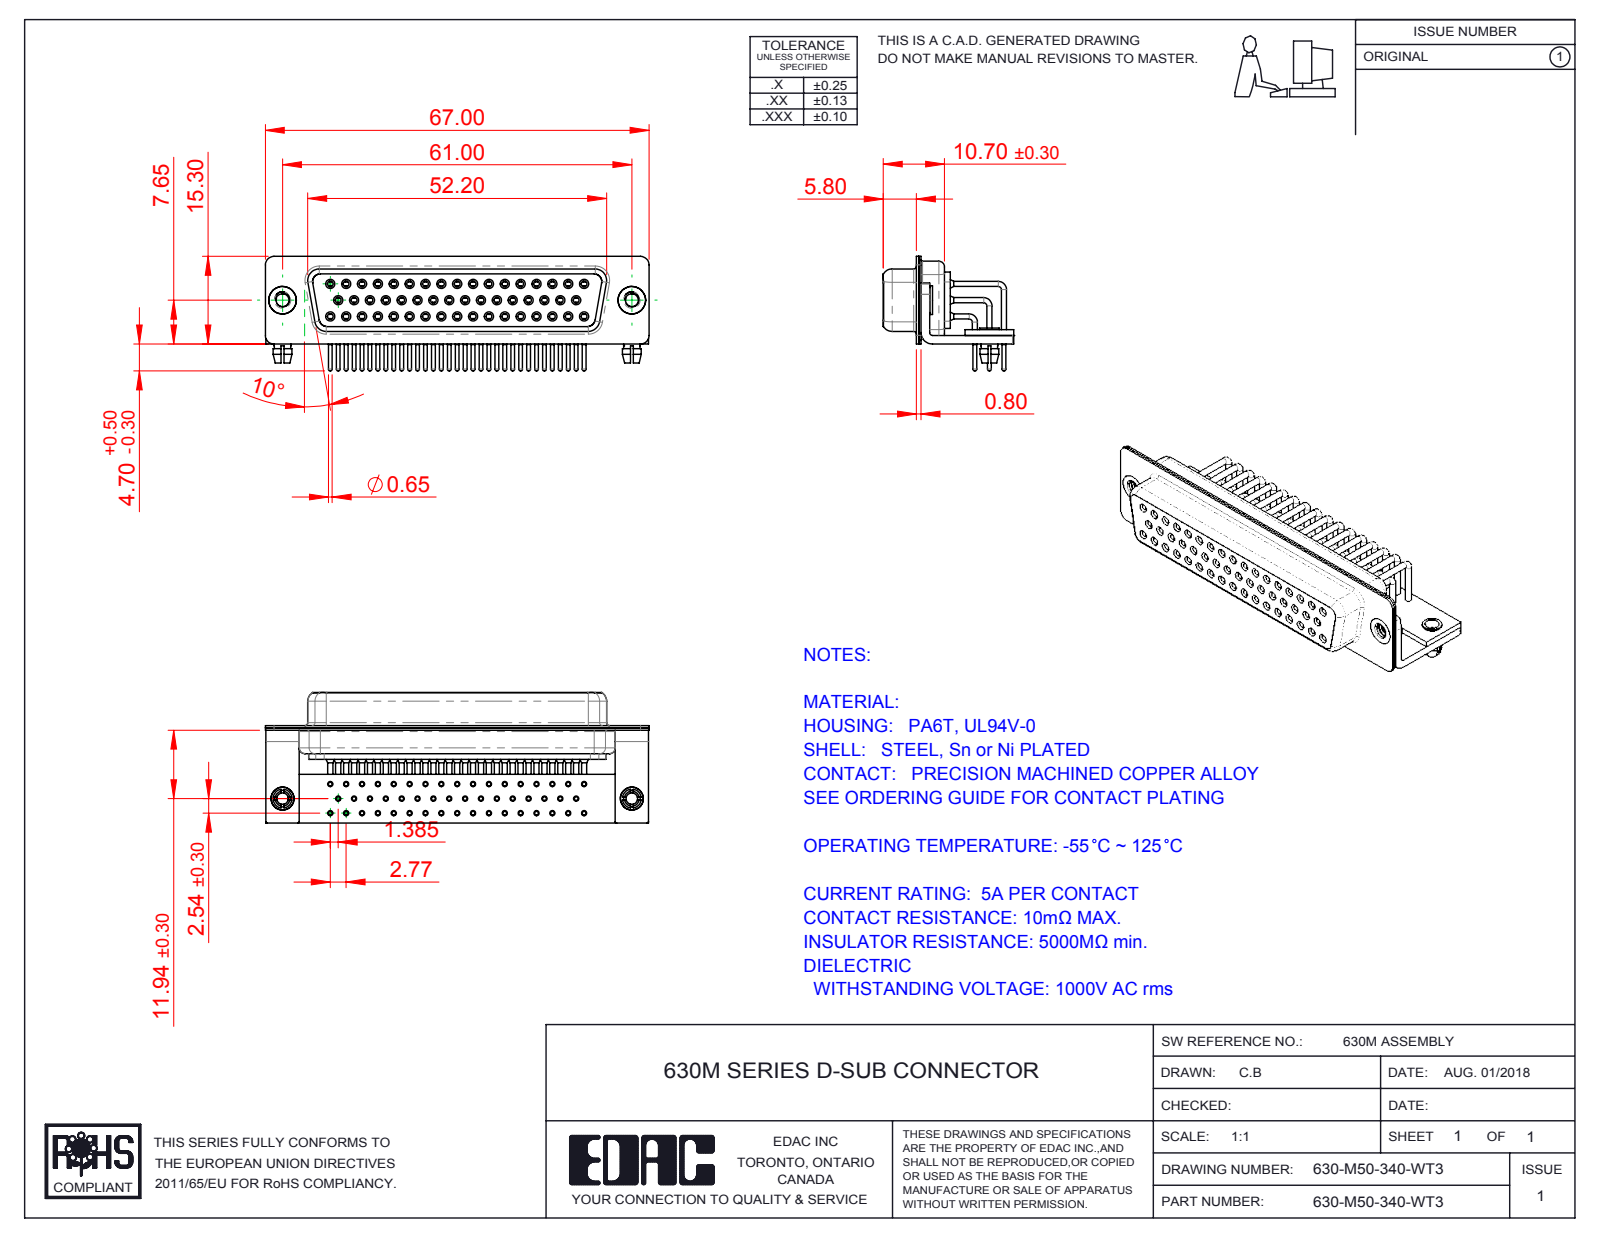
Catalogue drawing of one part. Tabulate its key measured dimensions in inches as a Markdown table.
| quantity | value |
| --- | --- |
| part name | 630M Stabilizer Bracket_50 Contacts; 630M Shell Rear_50 Contacts; 630M Housing_50 Contacts; 630M Contact Row 2_50 Contacts (+7 more) |
| STEP written by | SolidWorks 2016 (CONFIG_CONTROL_DESIGN) |
| units | inches |
| bodies | 60 solids, 3171 faces (891 planar, 1441 cylindrical, 839 other) |
| overall size | 2.638 × 0.898 × 0.787 |
| volume | 0.483 in³ |
| surface area | 29.21 in² |
| round holes (diameter × count) | 0.079 × 52, 0.035 × 50, 0.039 × 50, 0.043 × 50, 0.067 × 50, 0.071 × 50, 0.089 × 2, 0.098 × 2, 0.126 × 2, 0.157 × 2, 0.189 × 2 |
| round bosses / shafts (diameter × count) | 0.035 × 59, 0.063 × 50, 0.059 × 50, 0.026 × 50, 0.197 × 2, 0.193 × 2, 0.157 × 2, 0.134 × 2 |
| partial cylindrical surfaces (radius × count) | 0.01 × 16, 0.059 × 16, 0.079 × 13, 0.053 × 8, 0.063 × 8, 0.02 × 5, 0.024 × 4, 0.026 × 4 |
| main face-to-face distances | 0.016, 0.039, 0.087, 0.033, 0.053, 0.467, 0.482, 0.228, 0.232, 0.031 |
| hole center spacings | 0.109, 0.218, 0.327, 0.436, 0.545, 0.654, 0.124, 0.763 |
